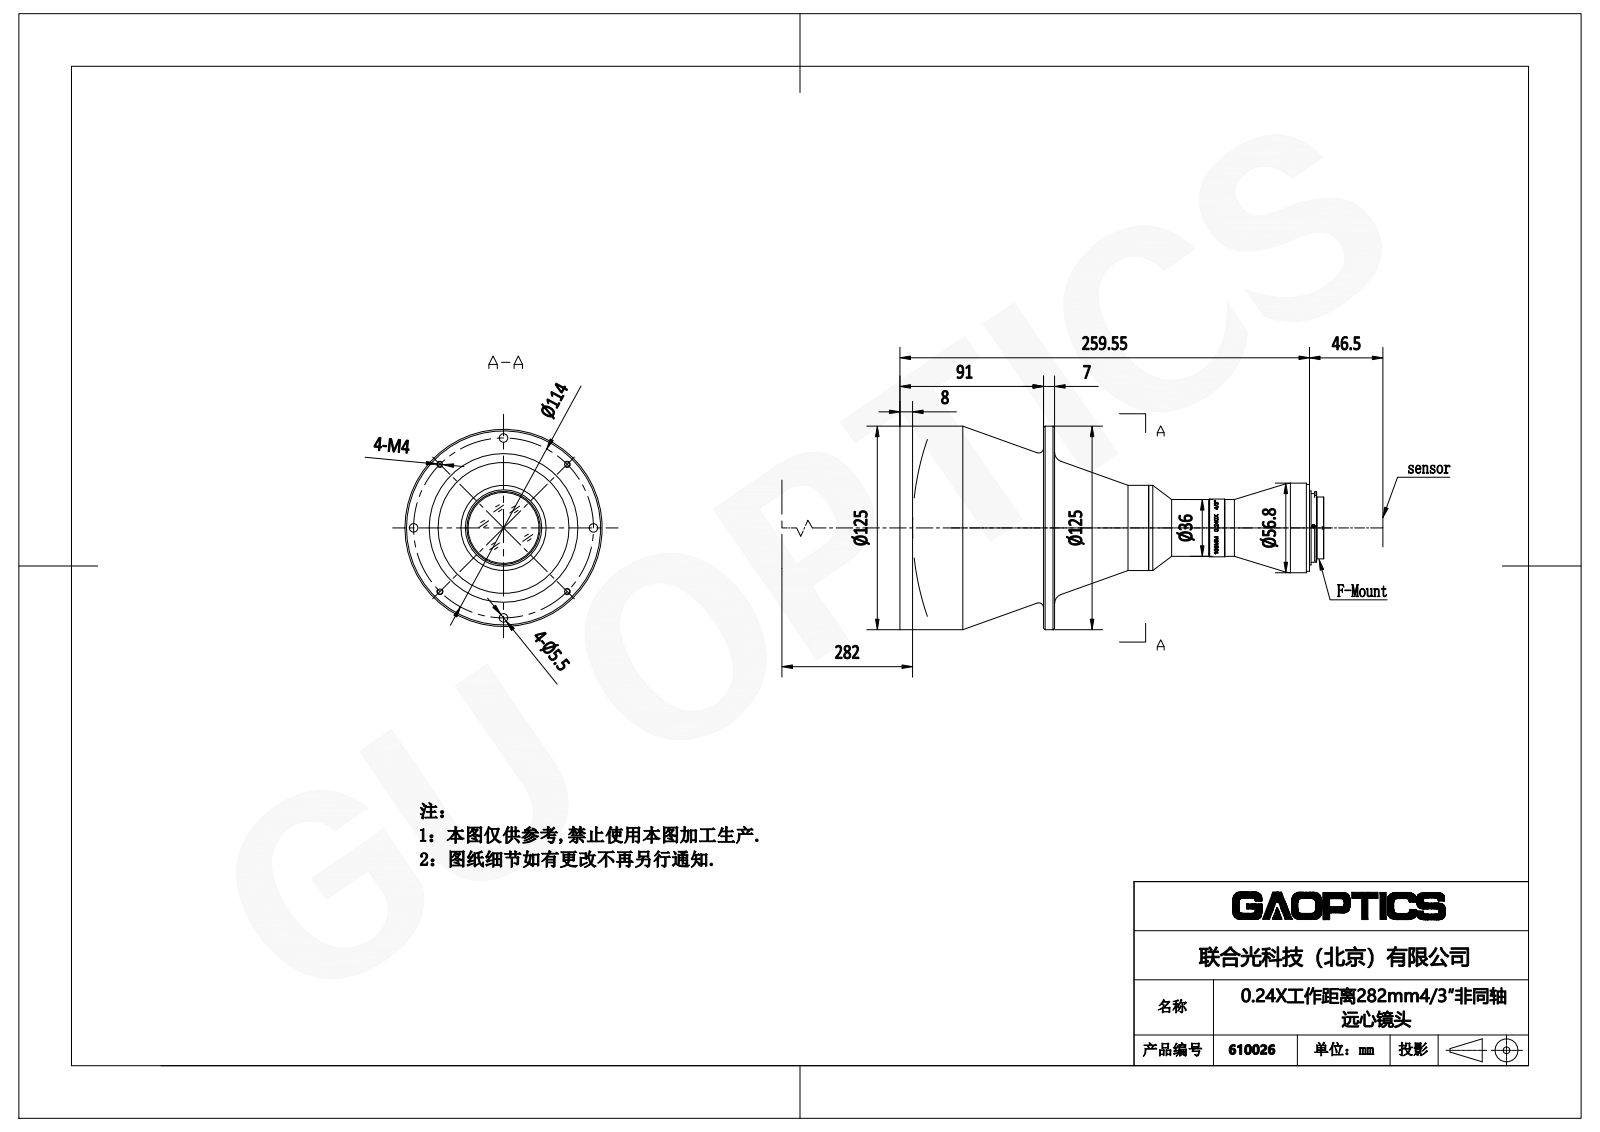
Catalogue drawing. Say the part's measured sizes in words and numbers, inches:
The part is named "610026". Its 3-D file was written by "SolidWorks 2020 (CONFIG_CONTROL_DESIGN)". It is 0 solids with 261 faces: 2 planar, 4 cylindrical and 255 other. Overall it measures 10.572 by 5.079 by 5.079 inches. Round bosses or shafts: 1 of diameter 1.259. The main face-to-face distances are 9.29.
